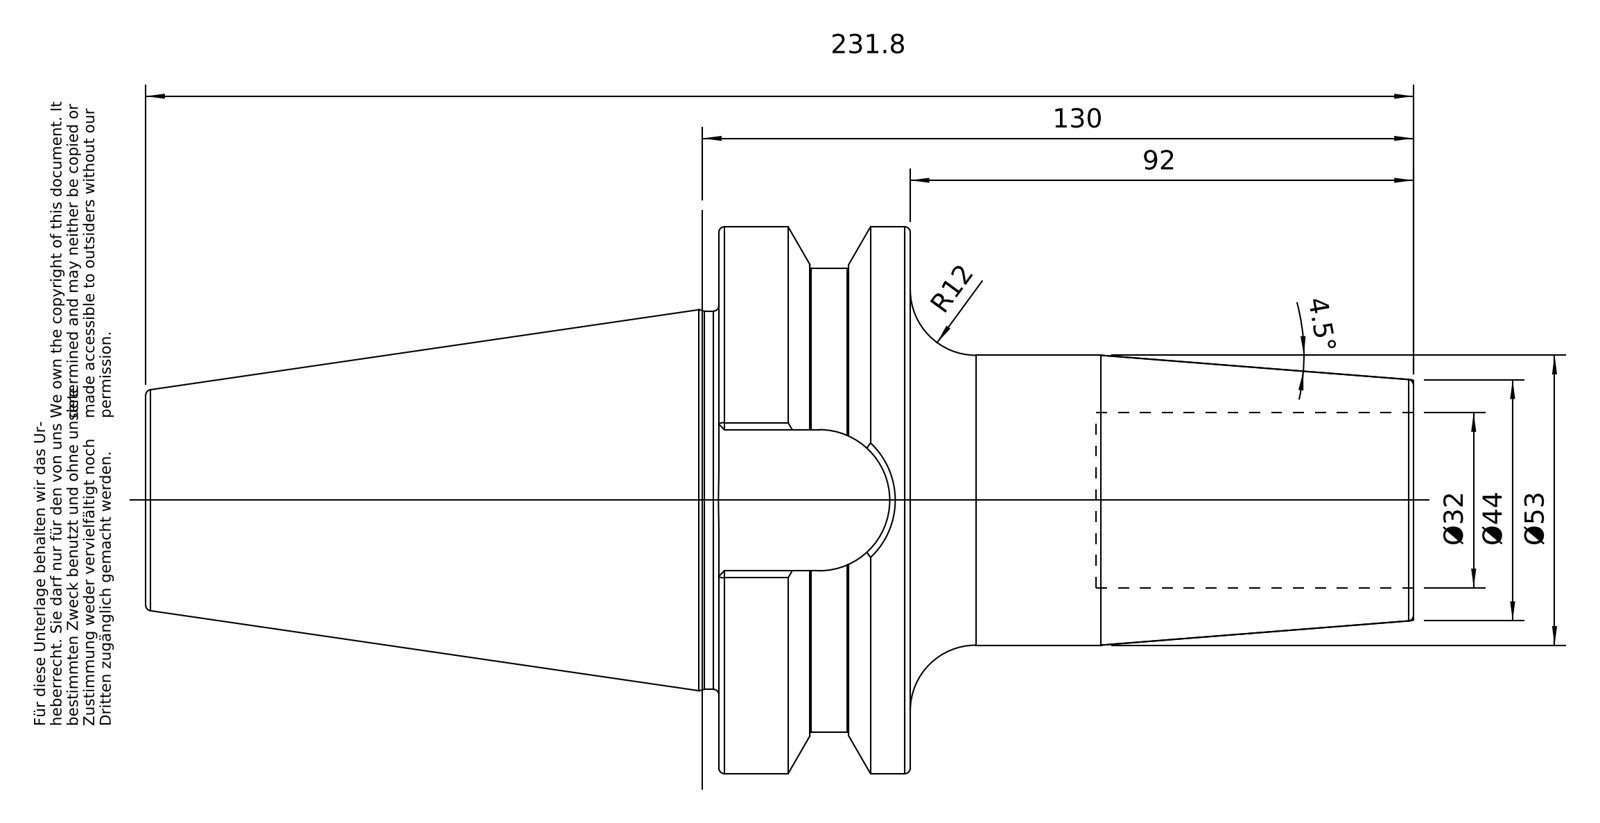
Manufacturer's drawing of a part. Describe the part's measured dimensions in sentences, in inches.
The part is named "50-644-32". Its 3-D file was written by "PRO/ENGINEER BY PARAMETRIC TECHNOLOGY CORPORATION, 2010430 (CONFIG_CONTROL_DESIGN)". It is 1 solid with 96 faces: 26 planar, 22 cylindrical and 48 other. Overall it measures 9.126 by 3.936 by 3.936 inches. Its volume is 37.21 cubic inches and its surface area 109.6 square inches. Round holes: 1 of diameter 0.817, 1 of diameter 0.985, 1 of diameter 1.012, 1 of diameter 1.26. Round bosses or shafts: 1 of diameter 3.936, 1 of diameter 3.337, 1 of diameter 2.722, 1 of diameter 2.087, 1 of diameter 0.945. Partial cylindrical surfaces (rounded edges, fillets, slot ends): 1 of radius 0.508. The main face-to-face distances are 1.378, 2.717, 1.339, 2.772, 5, 3.622, 2.283, 4.126, 5.504, 6.843.
